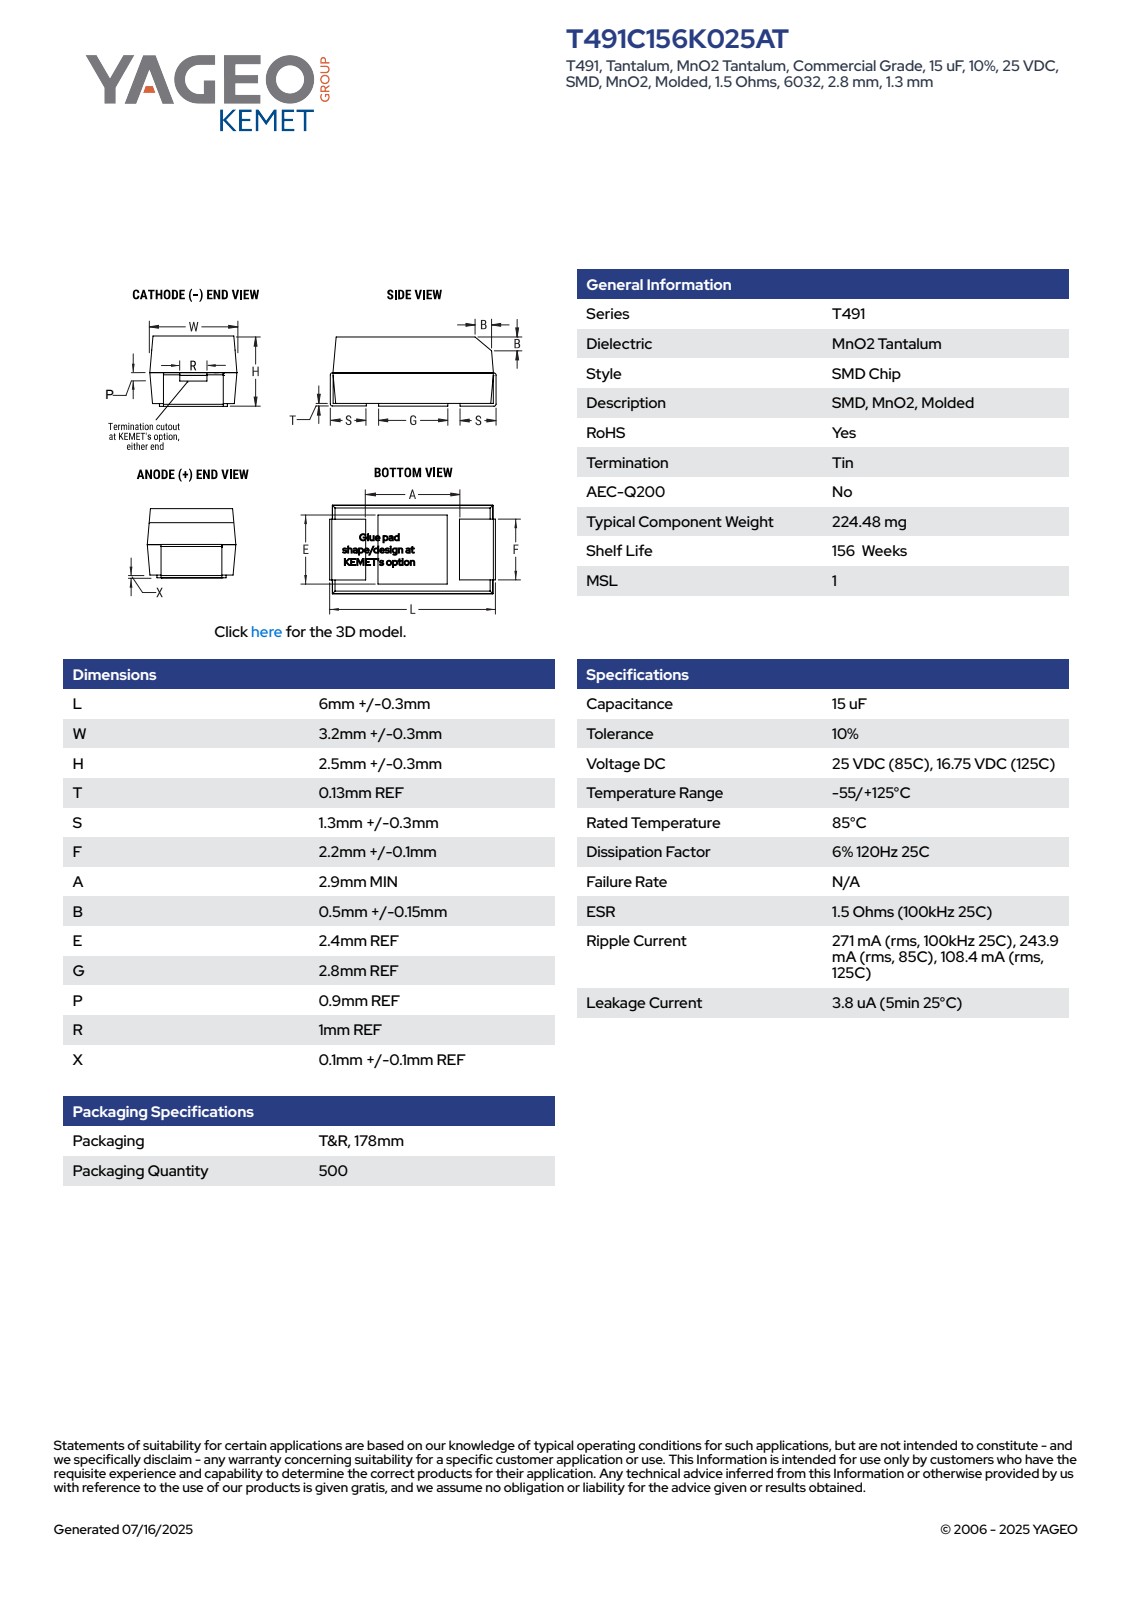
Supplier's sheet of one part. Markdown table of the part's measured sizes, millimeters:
| quantity | value |
| --- | --- |
| part name | CTSM_TCM2NK_6032_L6.3W3.5H2.8T0.13S1.3F2.3A2.9B0.65E2.4G2.8P0.9R1X0.2 |
| STEP written by | SolidWorks 2020 (AUTOMOTIVE_DESIGN) |
| units | millimeters |
| bodies | 4 solids, 100 faces (95 planar, 5 cylindrical, 0 other) |
| overall size | 6.3 × 3.5 × 2.81 |
| volume | 53 mm³ |
| surface area | 108 mm² |
| partial cylindrical surfaces (radius × count) | 0.1 × 4 |
| main face-to-face distances | 2.8, 2.6, 3.46, 3.47, 2.67, 6.17, 6.3, 6.04, 1.75, 4.55 |
